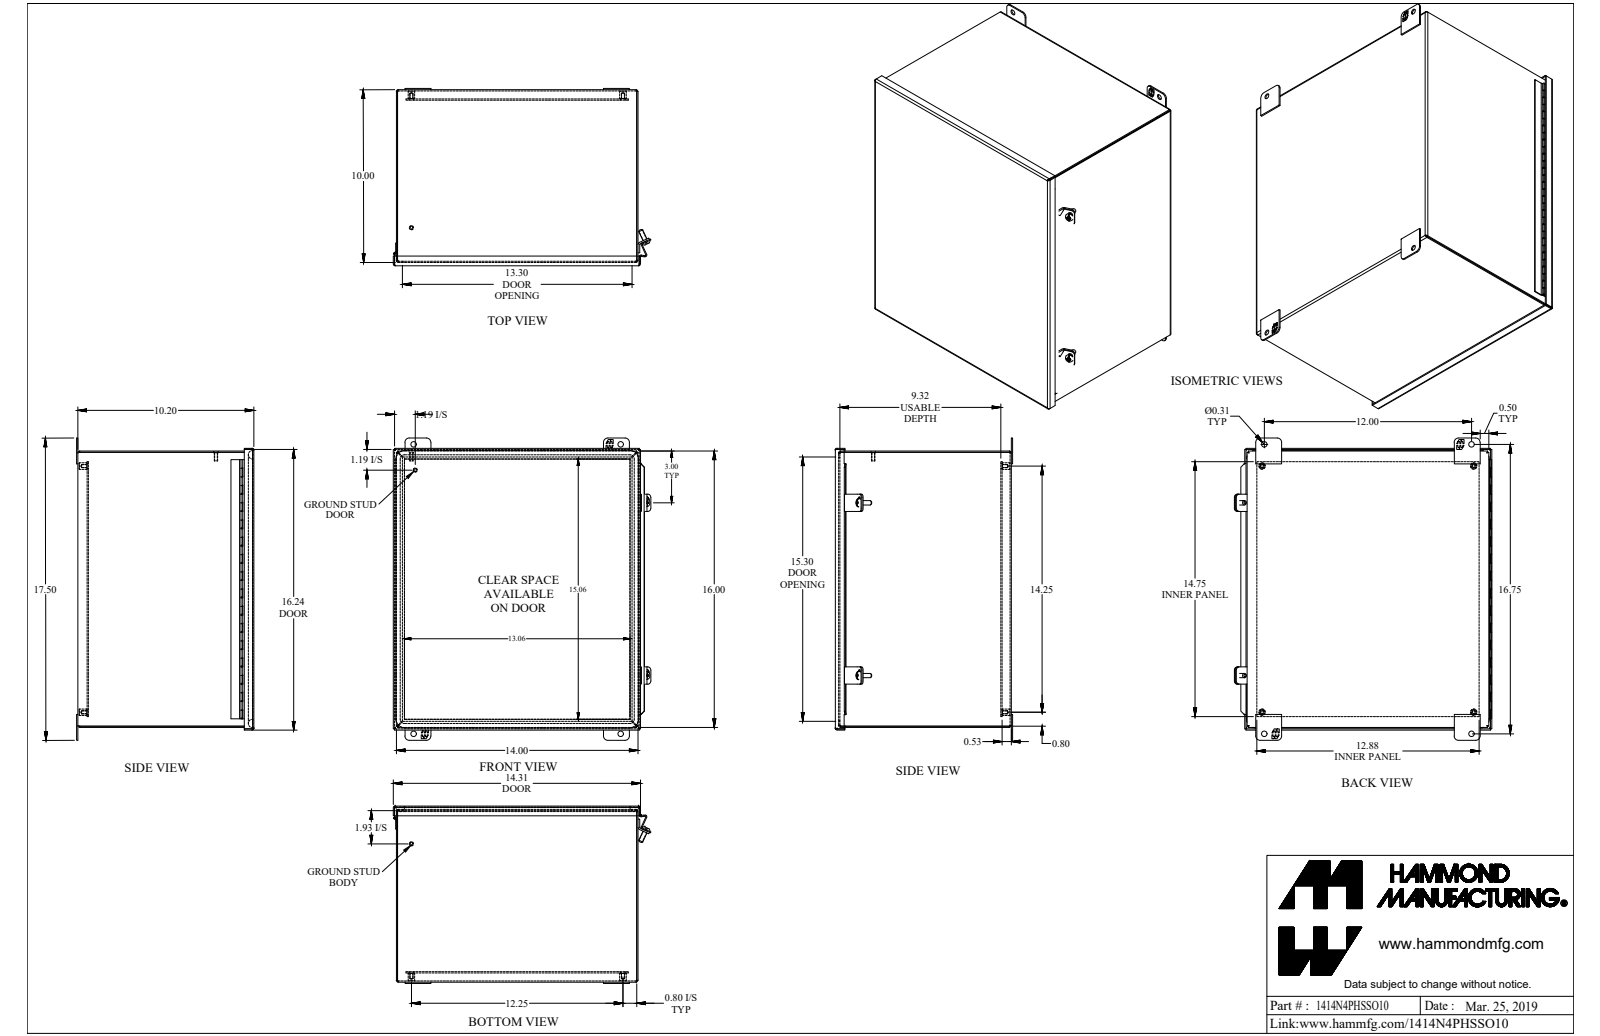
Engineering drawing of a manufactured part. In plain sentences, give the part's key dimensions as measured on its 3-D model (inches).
The part is named "1414N4PHSSO10". Its 3-D file was written by "SolidWorks 2018 (AUTOMOTIVE_DESIGN)". It is 21 solids with 780 faces: 496 planar, 220 cylindrical and 64 other. Overall it measures 17.5 by 14.903 by 10.269 inches. Its volume is 99.93 cubic inches and its surface area 2 797 square inches. Round holes: 4 of diameter 0.156, 4 of diameter 0.265, 4 of diameter 0.313, 2 of diameter 0.213, 1 of diameter 0.05. Round bosses or shafts: 4 of diameter 0.375, 4 of diameter 0.25, 2 of diameter 0.48, 2 of diameter 0.19, 1 of diameter 0.1, 1 of diameter 0.045. Partial cylindrical surfaces (rounded edges, fillets, slot ends): 24 of radius 0.25, 9 of radius 0.036, 9 of radius 0.108, 8 of radius 0.188, 4 of radius 0.007, 4 of radius 0.046, 4 of radius 0.079, 4 of radius 0.118. The main face-to-face distances are 0.072, 10.125, 9.593, 0.532, 13.928, 15.928, 10.197, 10.053, 0.604, 9.665. The hole center spacings are 12.189, 1.256, 15.5, 12.25, 12.25, 14.25, 14.25, 19.679.
